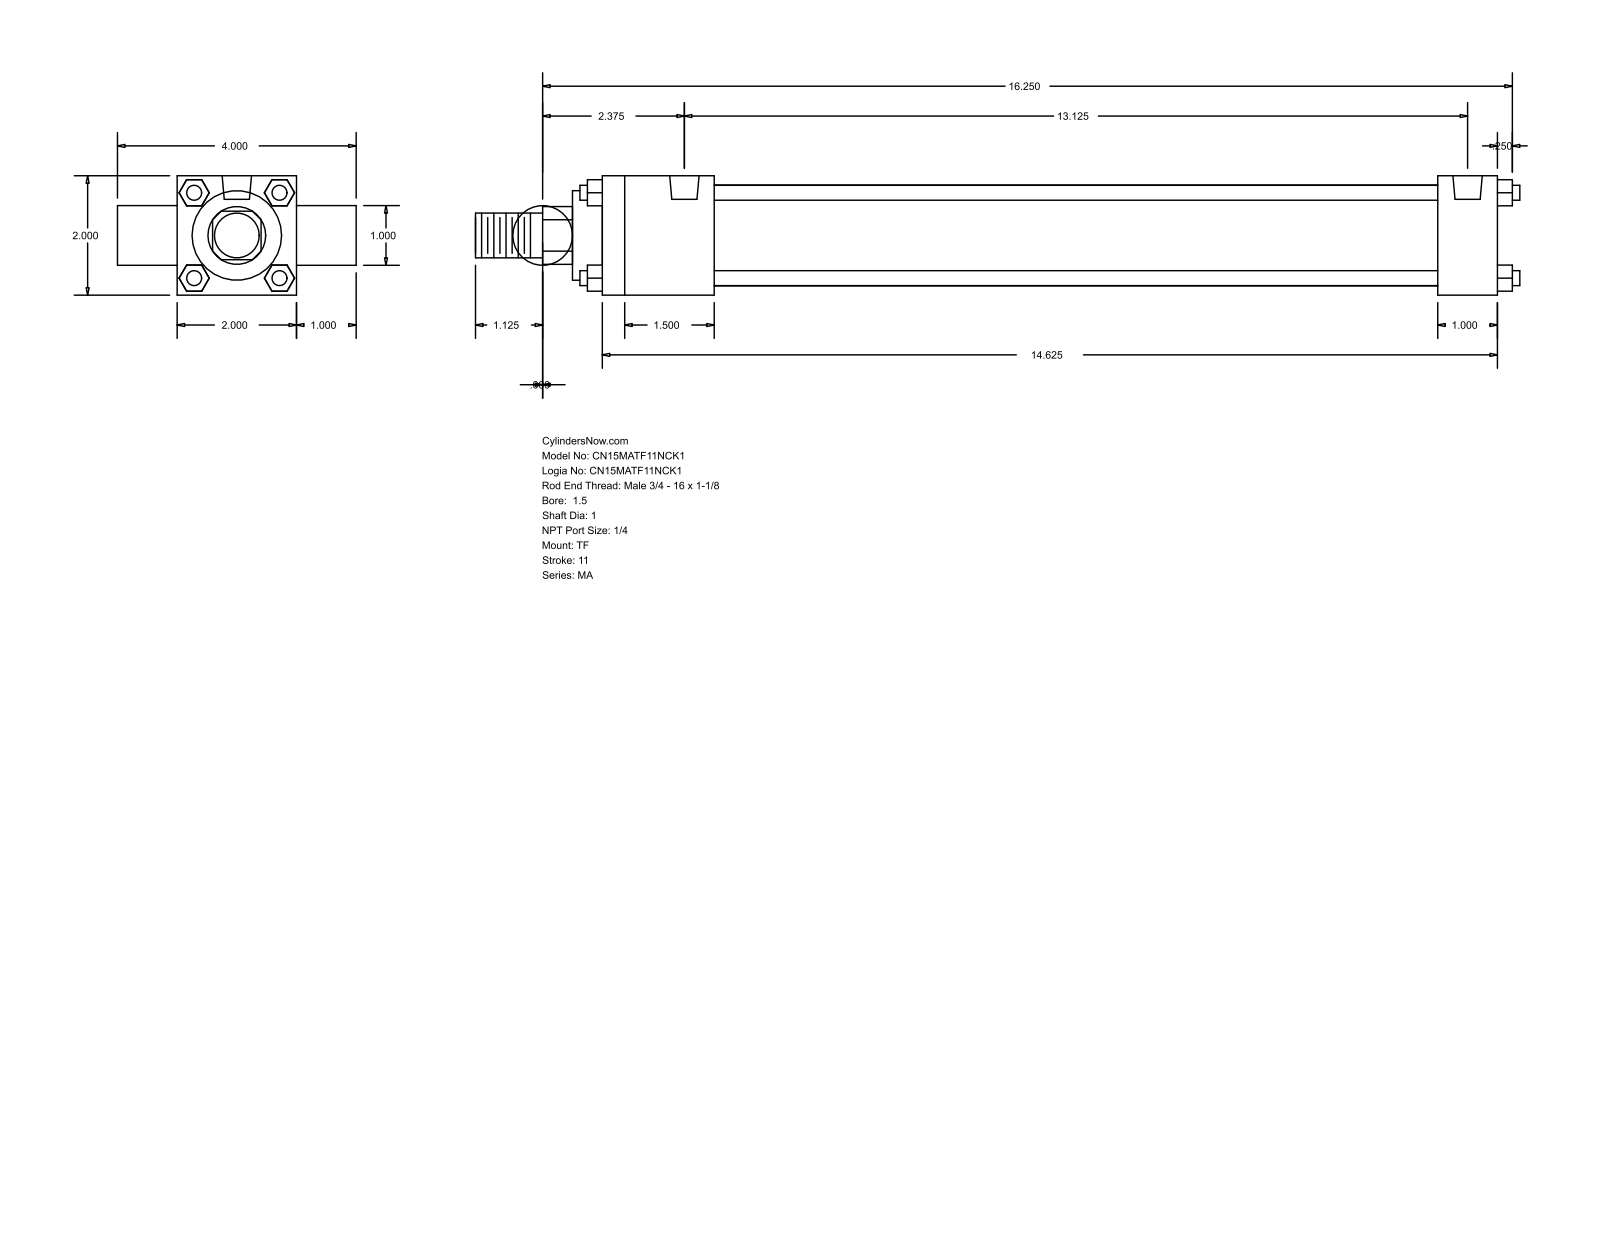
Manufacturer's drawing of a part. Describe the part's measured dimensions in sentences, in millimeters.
The part is named "MA_TF__0150_1". Its 3-D file was written by "GSSL Pune (CONFIG_CONTROL_DESIGN)". It is 0 solids with 120 faces: 92 planar, 28 cylindrical and 0 other. Overall it measures 444.5 by 101.6 by 50.8 millimeters. Round holes: 3 of diameter 7.94, 2 of diameter 12.49. Round bosses or shafts: 4 of diameter 6.35, 2 of diameter 25.4, 1 of diameter 42.93, 1 of diameter 38.1, 1 of diameter 19.05. Partial cylindrical surfaces (rounded edges, fillets, slot ends): 1 of radius 12.29. The main face-to-face distances are 50.8, 25.4, 381, 76.2, 6.35, 47.63, 355.6, 307.97, 333.37, 393.7. The hole center spacings are 333.37.
